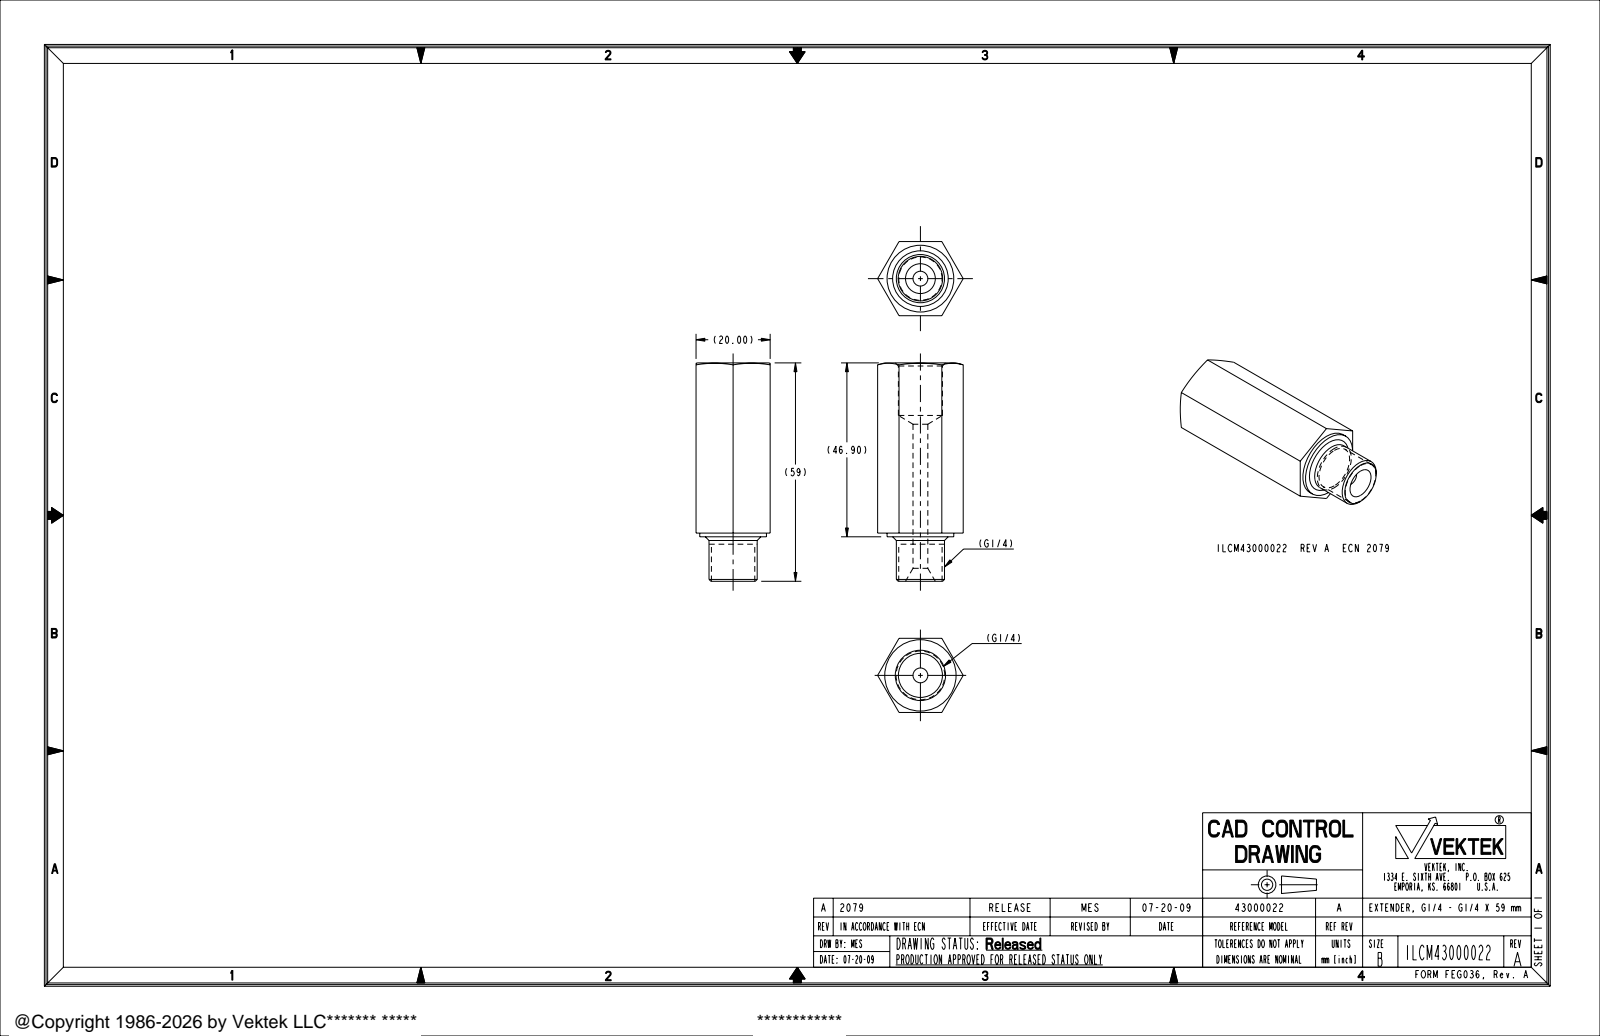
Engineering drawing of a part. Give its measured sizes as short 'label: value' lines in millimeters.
name: ILCM43000022
written by: PRO/ENGINEER BY PARAMETRIC TECHNOLOGY CORPORATION, 2007460 (AUTOMOTIVE_DESIGN_CC2)
unit: mm
bodies: 1 solid, 36 faces (12 planar, 12 cylindrical, 12 other)
size: 58.9 × 23.09 × 20
volume: 15 450 mm³; area: 6 272 mm²
holes: 1× ⌀4, 1× ⌀11.89
bosses: 1× ⌀18, 1× ⌀13.16, 1× ⌀13, 1× ⌀11.7
face distances: 20, 45.9, 1, 46.9, 12, 13, 58.9, 10, 2, 3
